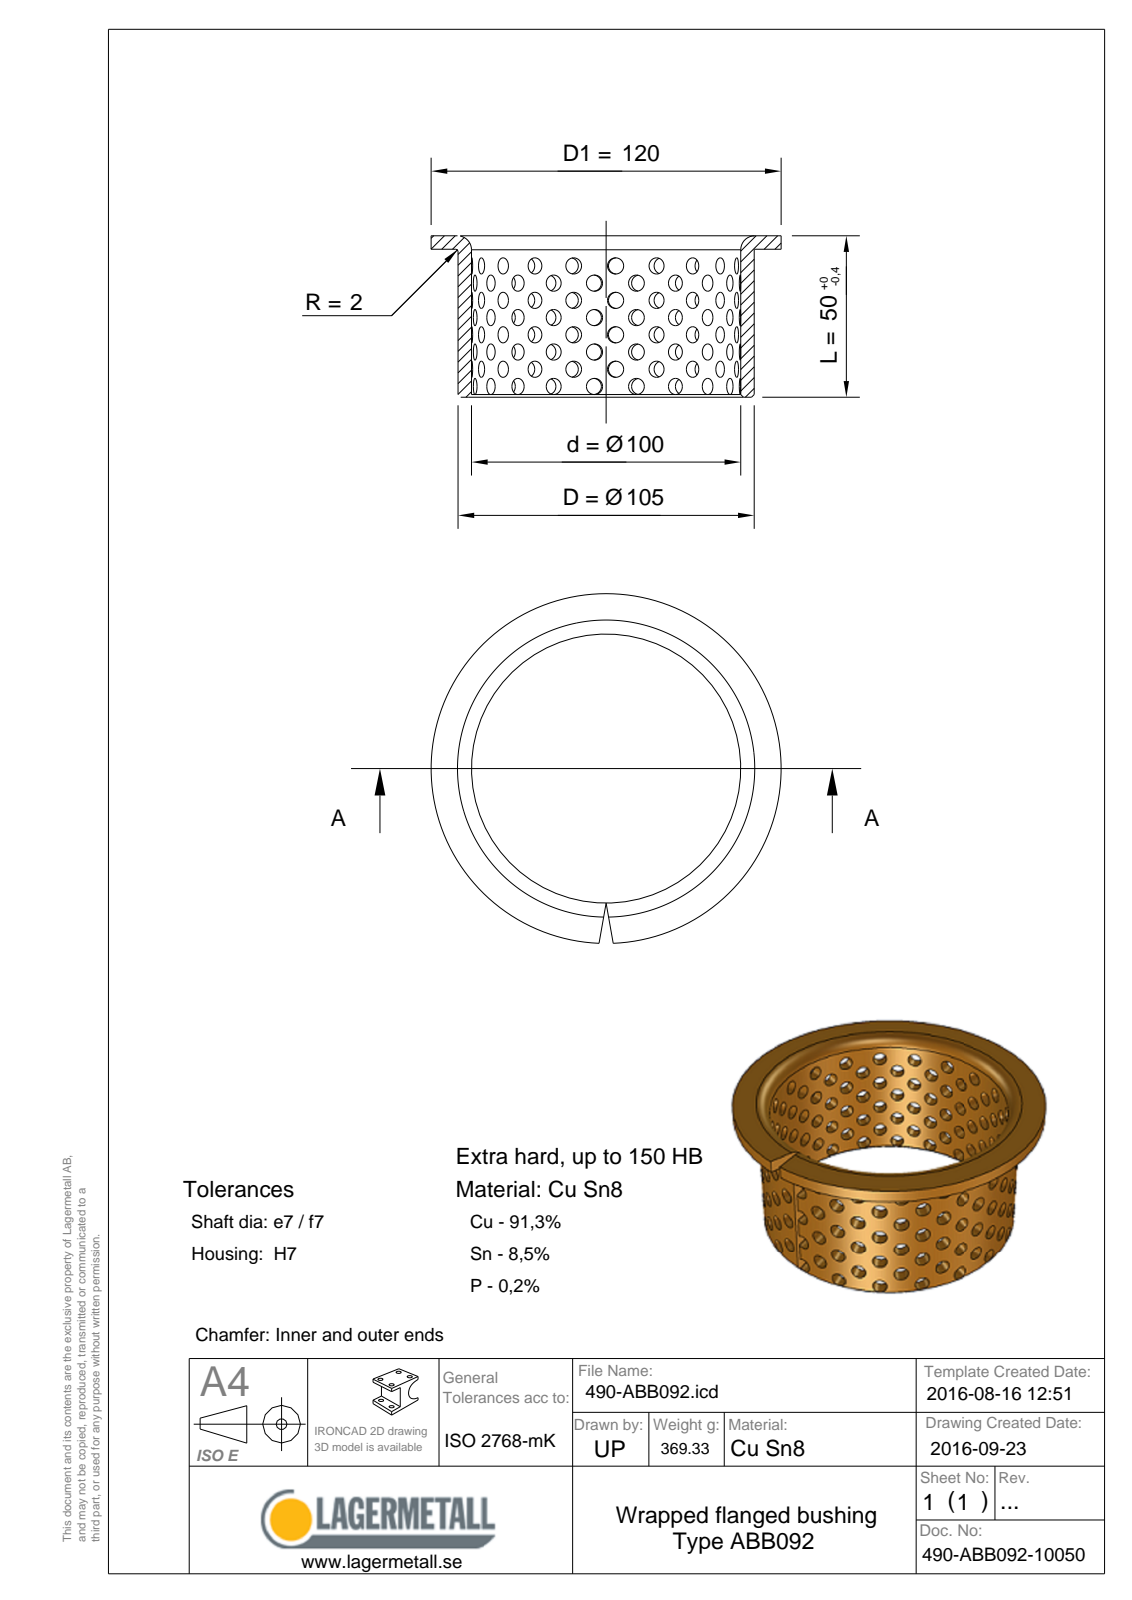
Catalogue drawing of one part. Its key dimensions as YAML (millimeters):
step_written_by: "Spatial InterOp 3D (CONFIG_CONTROL_DESIGN)"
units: millimeters
bodies: {solids: 1, faces: 26, planar: 5, cylindrical: 9, other: 12}
overall_size: [120, 120, 50]
volume: 45595
surface_area: 38361
round_holes:
  - {diameter: 100, count: 1}
round_bosses_or_shafts:
  - {diameter: 120, count: 1}
  - {diameter: 105, count: 1}
face_to_face_distances: [2.5, 47.5, 50]
